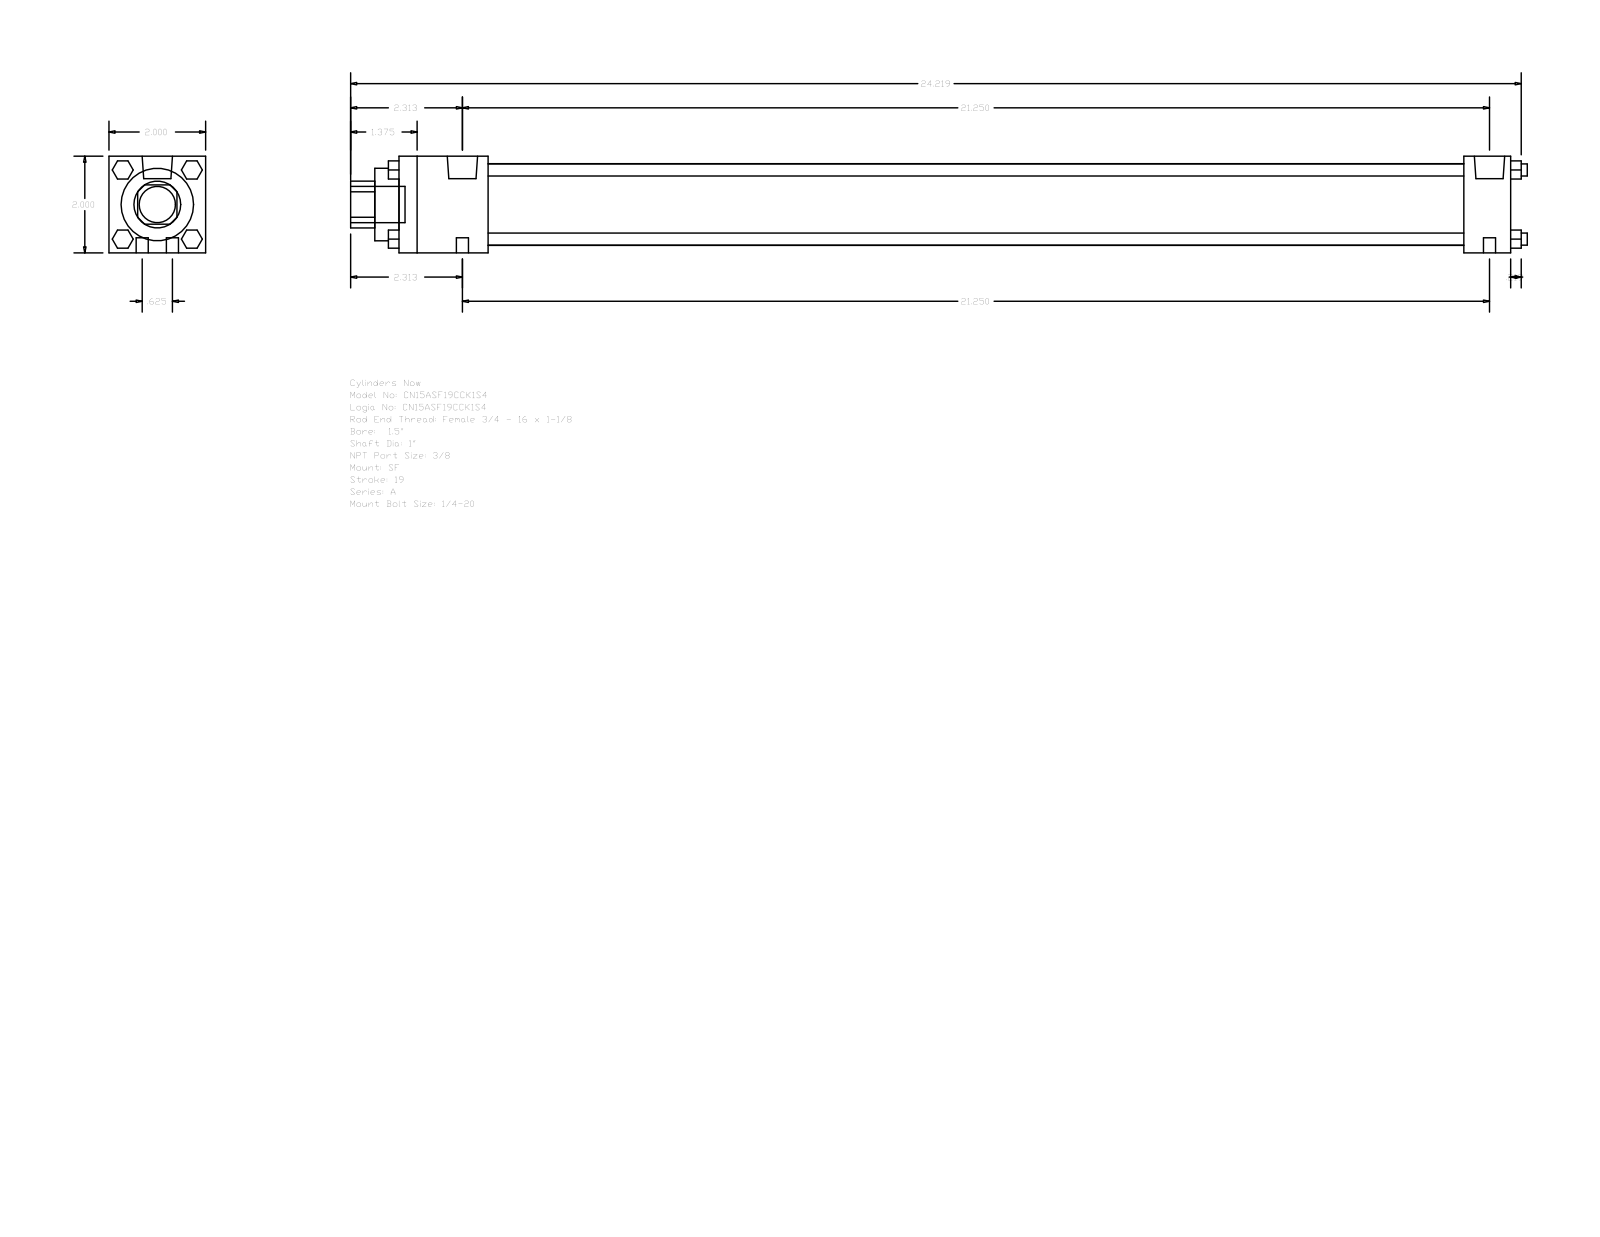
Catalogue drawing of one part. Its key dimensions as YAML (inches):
part_name: "A_SF__0150_1"
step_written_by: "GSSL Pune (CONFIG_CONTROL_DESIGN)"
units: inches
bodies: {solids: 0, faces: 124, planar: 94, cylindrical: 30, other: 0}
overall_size: [24.344, 2, 2]
round_holes:
  - {diameter: 1, count: 1}
  - {diameter: 1.5, count: 1}
  - {diameter: 1.69, count: 1}
round_bosses_or_shafts:
  - {diameter: 0.25, count: 8}
  - {diameter: 0.627, count: 2}
  - {diameter: 0.219, count: 2}
  - {diameter: 0.75, count: 1}
partial_cylinders:
  - {radius: 0.484, count: 1}
face_to_face_distances: [2, 23, 1.844, 22.031, 20.187, 21.156, 0.969, 0.5, 2.344, 22.531]
